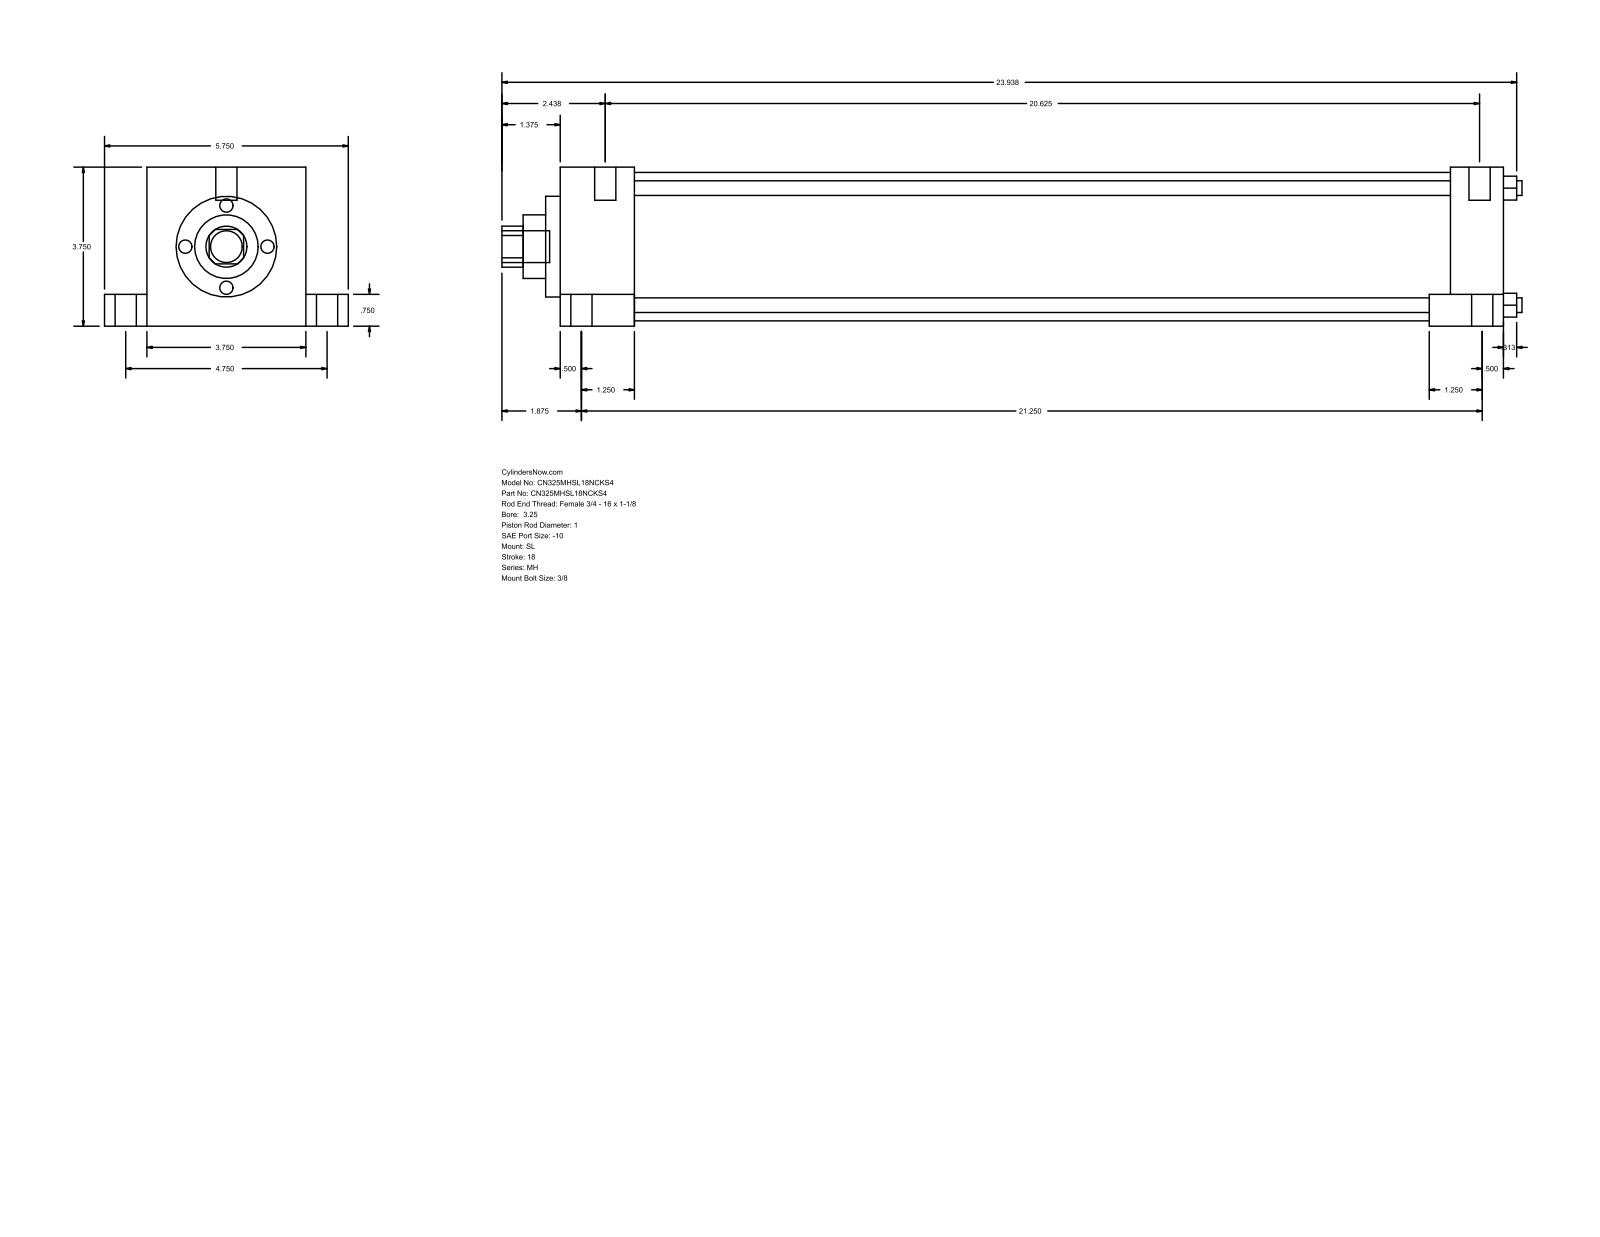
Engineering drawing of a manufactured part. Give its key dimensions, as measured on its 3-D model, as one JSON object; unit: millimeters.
{"part_name": "MH_SL__0325_1", "step_written_by": "GSSL Pune (CONFIG_CONTROL_DESIGN)", "units": "millimeters", "bodies": {"solids": 0, "faces": 110, "planar": 77, "cylindrical": 33, "other": 0}, "overall_size": [611.19, 146.05, 95.25], "round_holes": [[8.76, 4], [25.4, 1], [38.1, 1], [60.33, 1], [88.9, 1]], "round_bosses_or_shafts": [[12.7, 6], [19.05, 5], [5.56, 4]], "partial_cylinders_radius": [[12.29, 1]], "face_to_face_distances": [95.24, 565.16, 44.46, 520.7, 25.41, 120.65, 19.05, 76.19, 533.41, 488.95], "hole_center_spacings": [49.57, 70.1, 99.14]}
